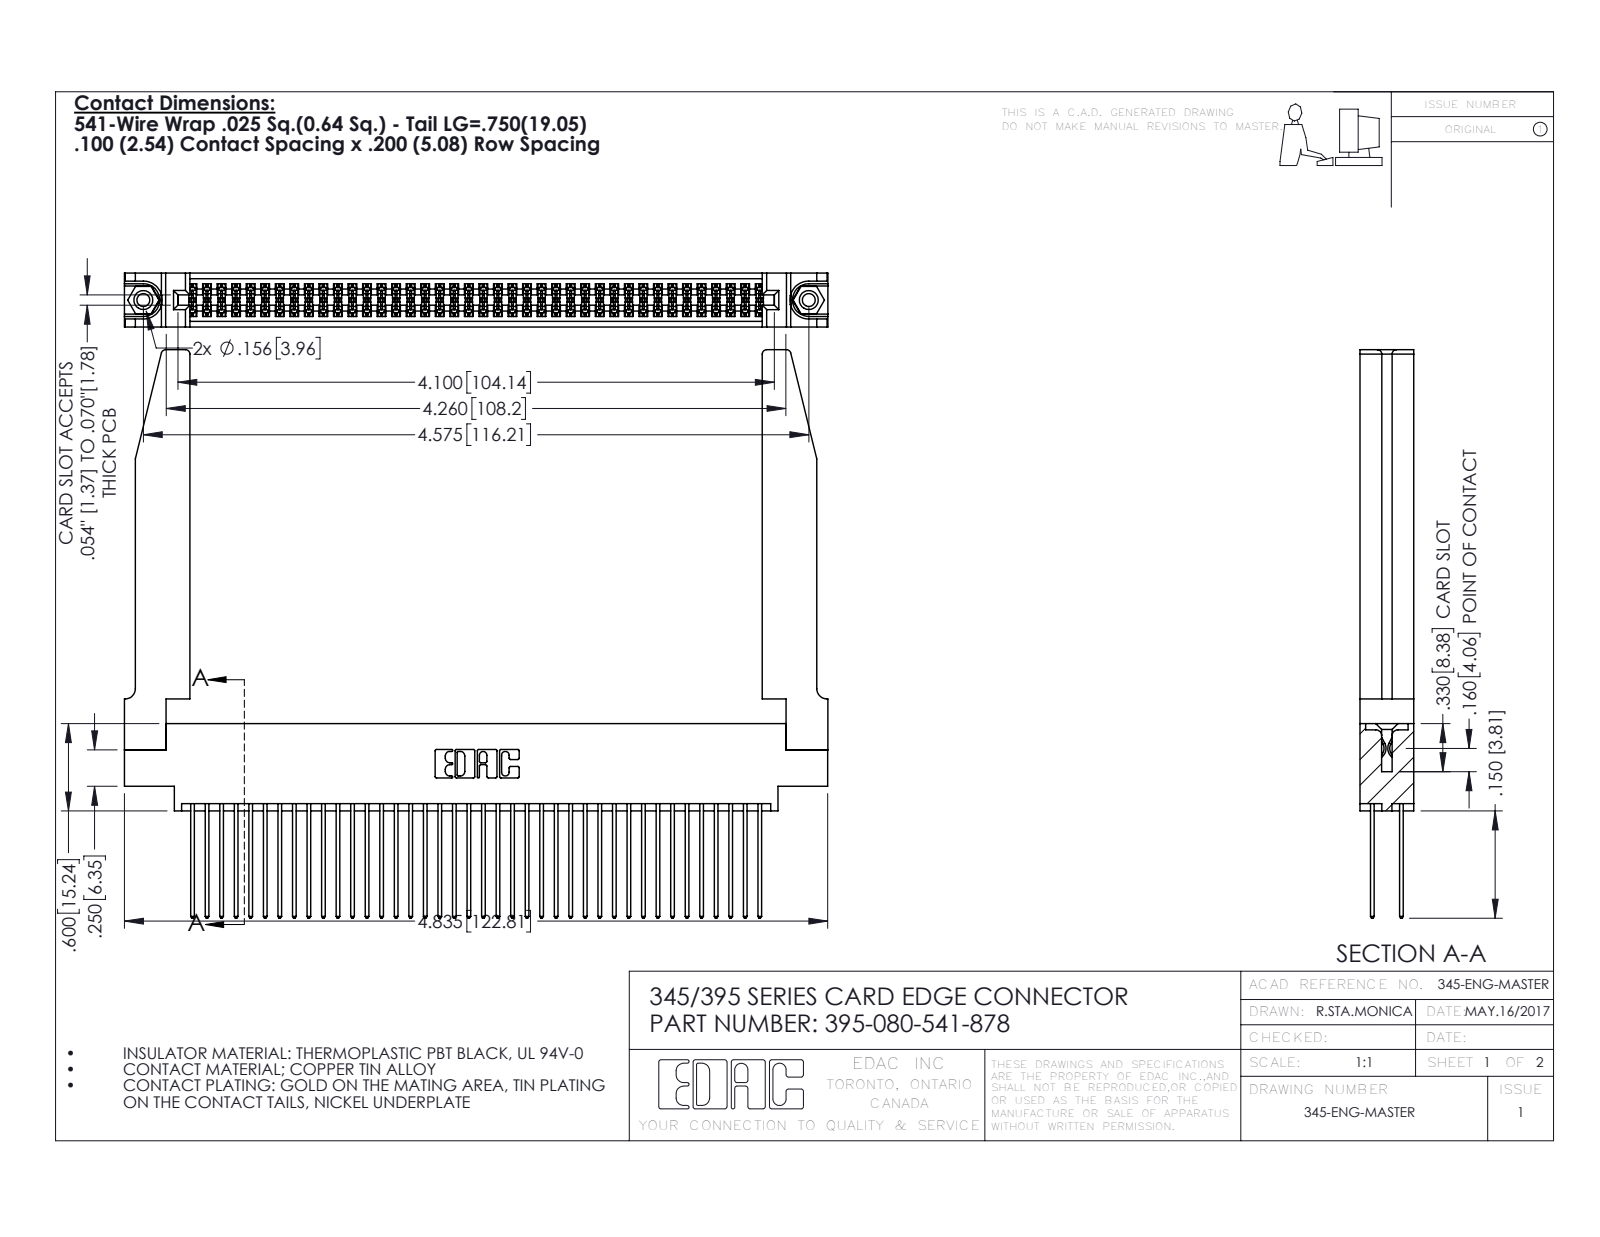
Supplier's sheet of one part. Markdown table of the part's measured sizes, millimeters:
| quantity | value |
| --- | --- |
| part name | 345-250-001_345-250-001-102; 345 Part_0.170 Offset - 0.156 Dia-TH; 345-220-078_345-220-078; 395-080-541-878 (+1 more) |
| STEP written by | SolidWorks 2016 (CONFIG_CONTROL_DESIGN) |
| units | millimeters |
| bodies | 85 solids, 4364 faces (2866 planar, 1446 cylindrical, 52 other) |
| overall size | 122.8 × 99.2 × 9.4 |
| volume | 20 020 mm³ |
| surface area | 27 220 mm² |
| round holes (diameter × count) | 2.3 × 2, 3.2 × 2, 4 × 2, 1.6 × 1 |
| round bosses / shafts (diameter × count) | 3.9 × 2 |
| partial cylindrical surfaces (radius × count) | 0.2 × 120, 0.3 × 80, 0.3 × 22, 0.8 × 8, 0.2 × 6, 0.8 × 6, 0.7 × 3, 0.4 × 2 |
| main face-to-face distances | 1.8, 7.6, 9.4, 2.5, 6.9, 0.6, 5.1, 5.7, 4.4, 3.8 |
| hole center spacings | 6.9, 110.2, 116.2 |
